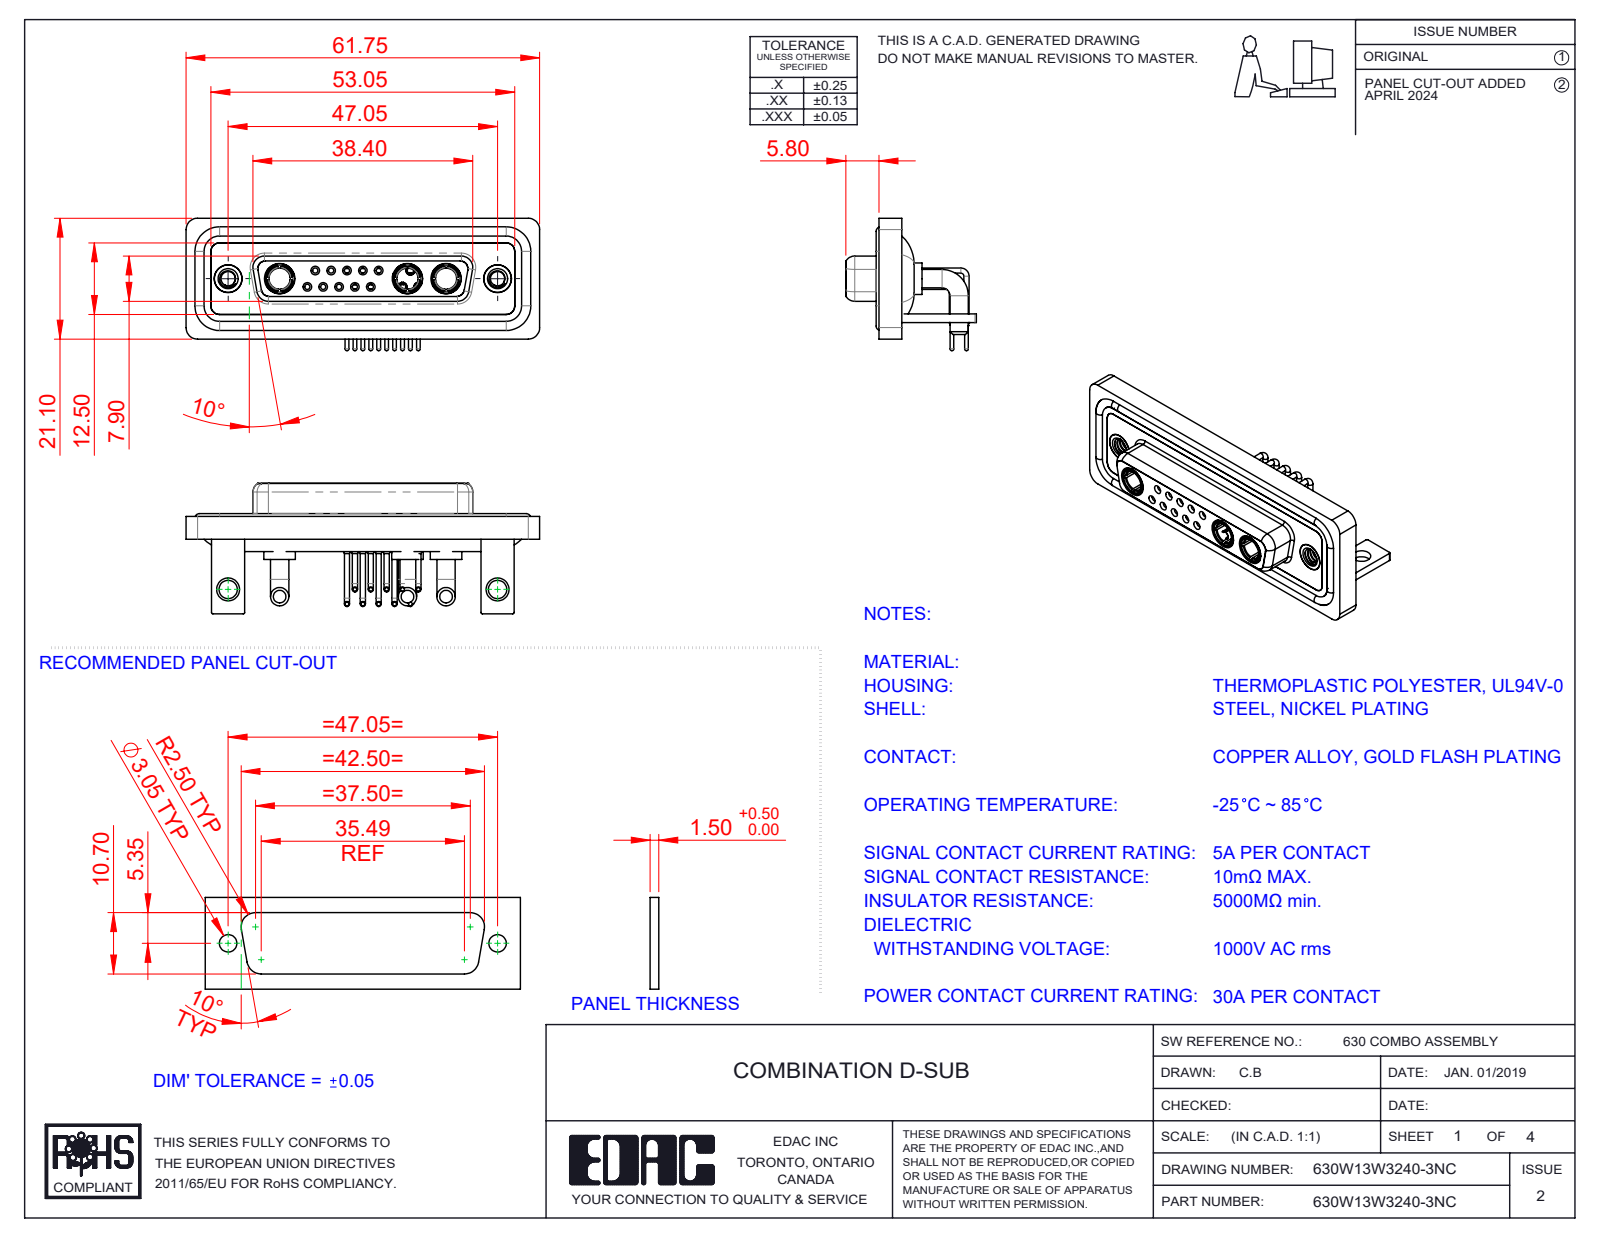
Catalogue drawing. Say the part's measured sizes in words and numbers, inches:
The part is named "630Combo Shell Front_25 Contacts; 630Combo Housing_13W3; 630W13W3240-3NC; 630Combo Contact Row 2_50 Contacts (+6 more)". Its 3-D file was written by "SolidWorks 2023 (CONFIG_CONTROL_DESIGN)". It is 25 solids with 1192 faces: 362 planar, 515 cylindrical and 315 other. Overall it measures 2.431 by 0.91 by 0.898 inches. Its volume is 0.544 cubic inches and its surface area 23.39 square inches. Round holes: 10 of diameter 0.035, 10 of diameter 0.043, 10 of diameter 0.059, 10 of diameter 0.079, 5 of diameter 0.063, 5 of diameter 0.067, 5 of diameter 0.191, 3 of diameter 0.146, 3 of diameter 0.209, 2 of diameter 0.098, 2 of diameter 0.126, 2 of diameter 0.157. Round bosses or shafts: 15 of diameter 0.035, 12 of diameter 0.063, 10 of diameter 0.026, 6 of diameter 0.126, 5 of diameter 0.079, 5 of diameter 0.059, 3 of diameter 0.217, 3 of diameter 0.205. Partial cylindrical surfaces (rounded edges, fillets, slot ends): 19 of radius 0.079, 18 of radius 0.059, 16 of radius 0.01, 8 of radius 0.053, 8 of radius 0.063, 5 of radius 0.02, 4 of radius 0.024, 4 of radius 0.026. The main face-to-face distances are 0.016, 0.071, 0.114, 0.146, 0.059, 0.161, 0.043, 0.055, 0.063, 0.122. The hole center spacings are 0.124, 0.109, 0.218, 0.198, 0.327, 0.198, 0.295, 0.436.
